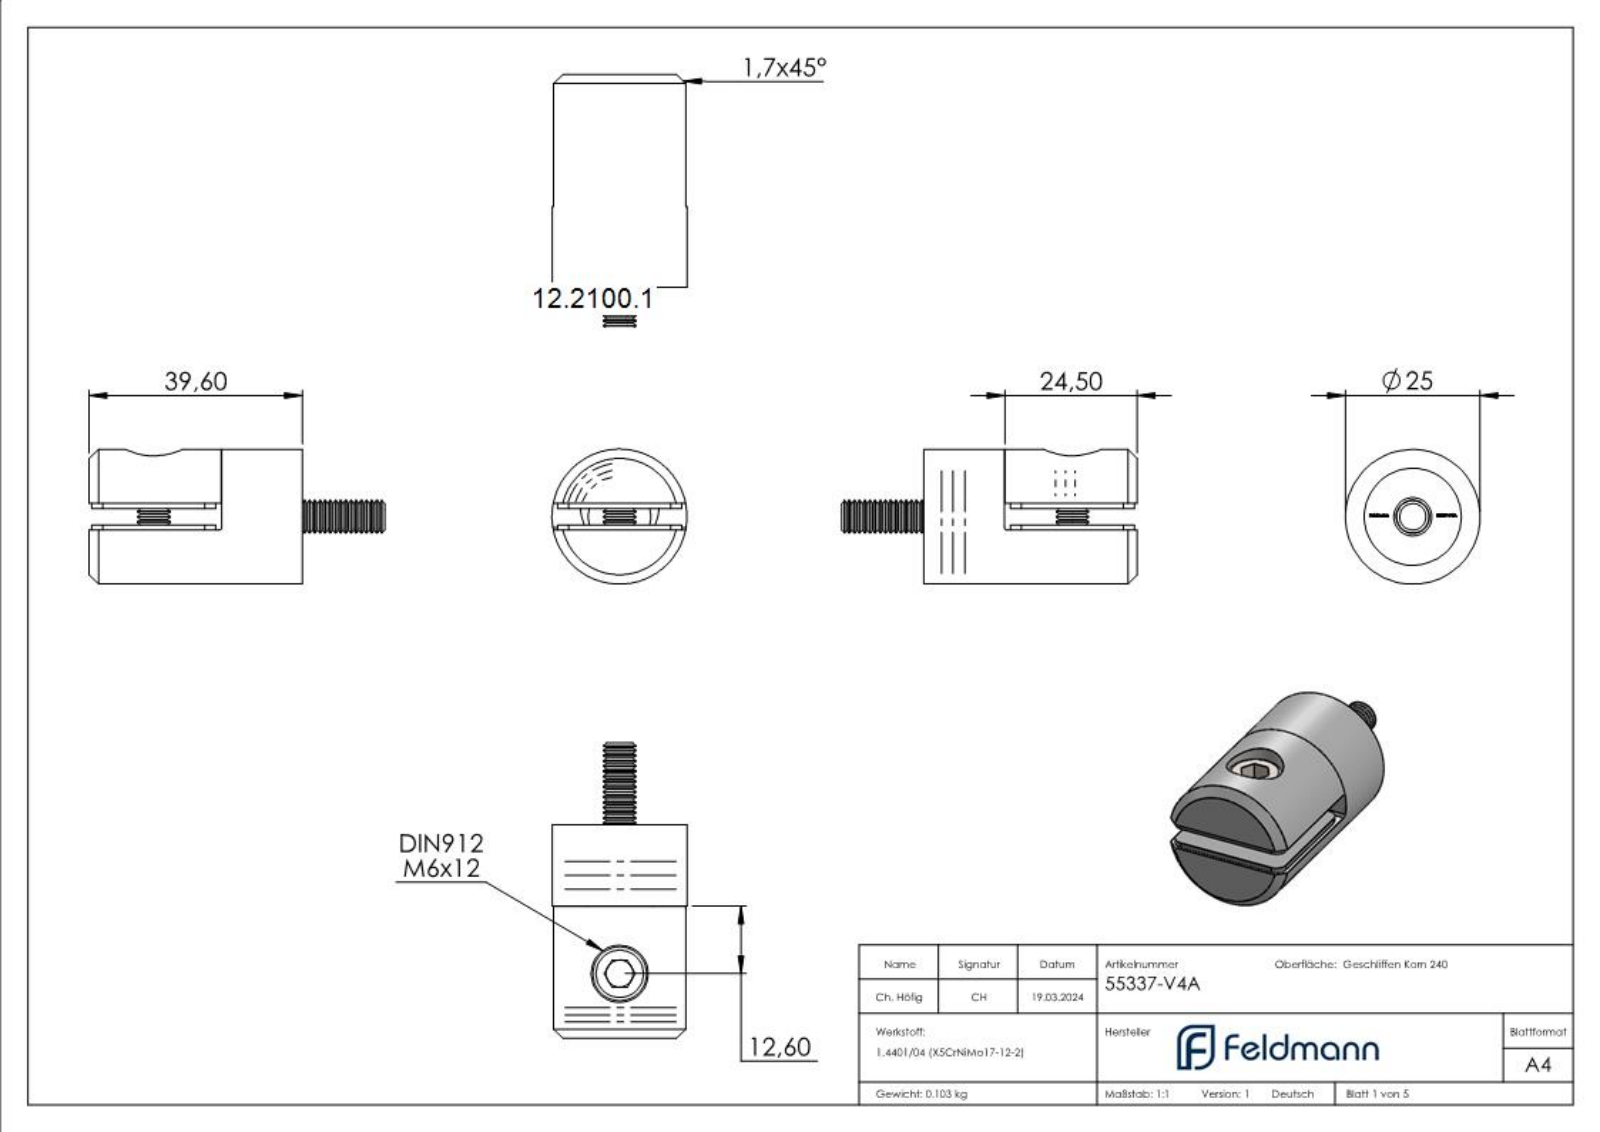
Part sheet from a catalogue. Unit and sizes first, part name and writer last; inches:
Units: inches
Overall size (bounding box): 2.161 × 0.984 × 0.984
Round holes (diameter × count): ⌀0.157 ×2, ⌀0.197 ×1, ⌀0.256 ×1, ⌀0.276 ×1, ⌀0.28 ×1, ⌀0.417 ×1, ⌀0.575 ×1, ⌀0.709 ×1
Round bosses / shafts (diameter × count): ⌀0.236 ×2, ⌀0.984 ×1, ⌀0.456 ×1, ⌀0.394 ×1
Partial cylindrical surfaces — rounded edges, fillets, slot ends (radius × count): R0.008 ×40, R0.079 ×6, R0.049 ×2, R0.02 ×1
Main face-to-face distances: 0.157, 0.039, 0.197, 0.118, 1.559, 0.201, 1.358, 0.394, 0.594, 0.965
Hole centre spacings: 0.369, 0.472
Volume: 0.92 in³ · Surface area: 16 in²
Bodies: 6 solids, 705 faces (228 planar, 186 cylindrical, 291 other)
Part name (STEP PRODUCT): 5533X-240 Teil2_5533X-240 Teil2; 5533x-240 Teil3_5533x-240 Teil3; 55337-V4A; 5533X-240 Teil1_55337-V4A Teil1 (+2 more)
STEP written by: SolidWorks 2018 (CONFIG_CONTROL_DESIGN)
